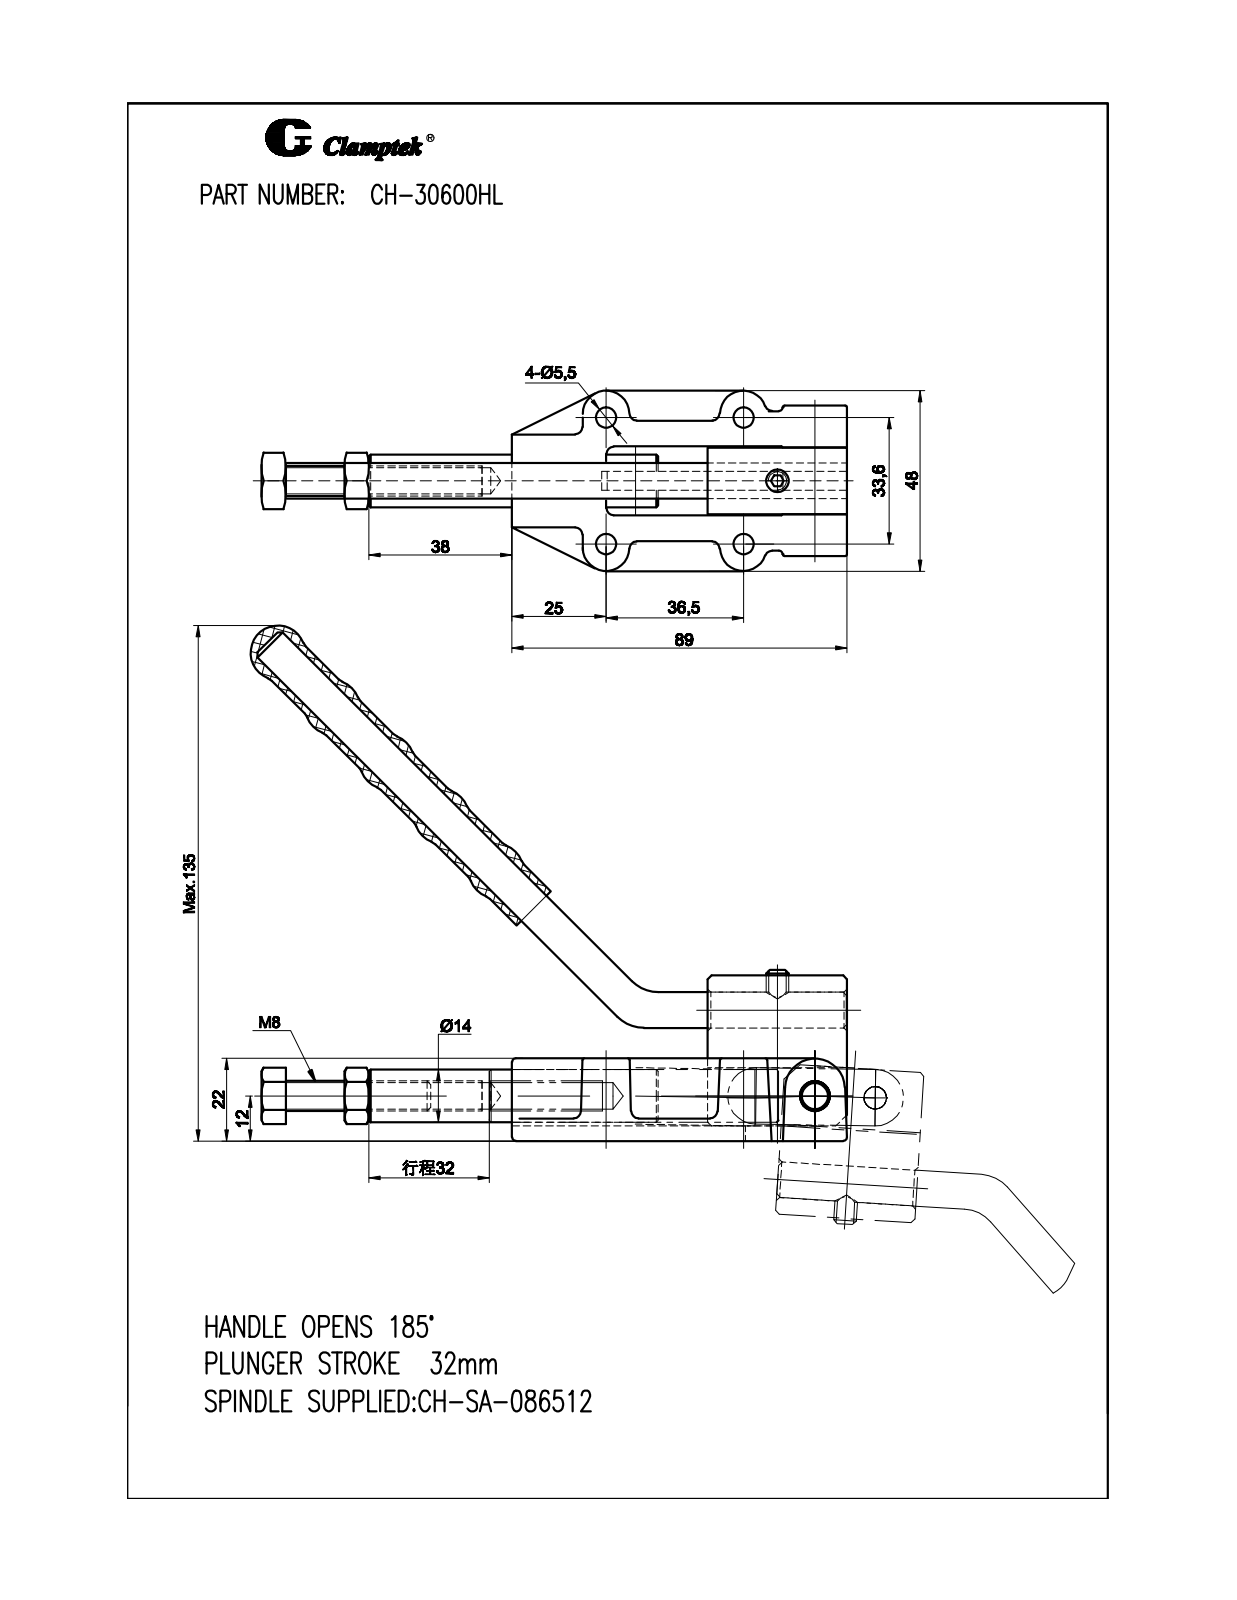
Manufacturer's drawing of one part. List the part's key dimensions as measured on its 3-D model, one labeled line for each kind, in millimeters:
Part name (STEP PRODUCT): CH-30600HL
STEP written by: SolidWorks 2008 (CONFIG_CONTROL_DESIGN)
Units: millimetres
Bodies: 13 solids, 1536 faces (701 planar, 562 cylindrical, 273 other)
Overall size (bounding box): 157.31 × 134.57 × 46.6
Volume: 98 538 mm³ · Surface area: 51 405 mm²
Round holes (diameter × count): ⌀5.5 ×4, ⌀6 ×2, ⌀5.2 ×1, ⌀6.8 ×1, ⌀7 ×1, ⌀8 ×1, ⌀9.3 ×1, ⌀9.5 ×1, ⌀13.9 ×1
Round bosses / shafts (diameter × count): ⌀12.3 ×1, ⌀9.5 ×1, ⌀8 ×1, ⌀5.9 ×1
Partial cylindrical surfaces — rounded edges, fillets, slot ends (radius × count): R0.1 ×124, R0.15 ×72, R1 ×27, R2 ×16, R1.5 ×5, R6.5 ×4, R7.5 ×2, R8 ×1
Main face-to-face distances: 6.05, 10.95, 17, 4.9, 22, 4, 18, 21.99, 43.99, 39.99
Hole centre spacings: 18.83, 19.06, 33.6, 36.5, 48.03, 48.5, 49.61, 0.5
